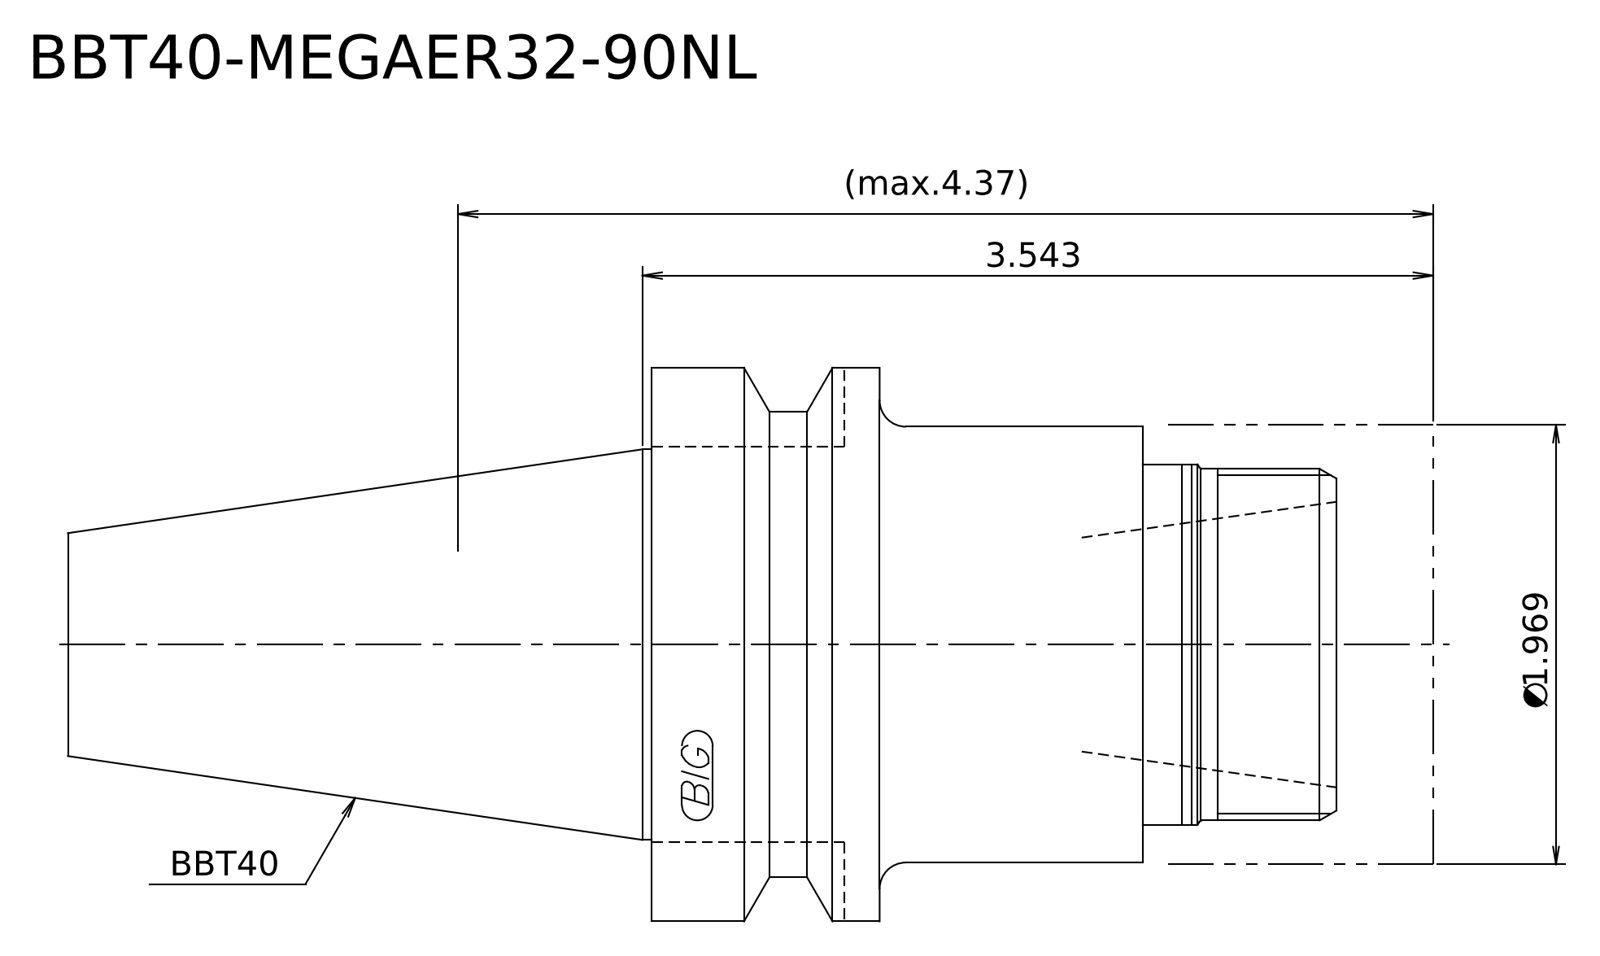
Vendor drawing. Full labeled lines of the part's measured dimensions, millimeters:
STEP written by: Kubotek KeyCreator 2011 V10.0.2 (22737) (automotive_design)
Units: millimetres
Bodies: 2 solids, 21 faces (6 planar, 8 cylindrical, 7 other)
Overall size (bounding box): 155.4 × 63 × 63
Volume: 286 061 mm³ · Surface area: 34 285 mm²
Round bosses / shafts (diameter × count): ⌀63 ×1, ⌀53 ×1, ⌀50 ×1, ⌀49.6 ×1, ⌀44.45 ×1, ⌀41 ×1, ⌀40 ×1
Main face-to-face distances: 30.2, 89, 58.8, 11, 19.2, 78, 33, 22, 2.8, 56
